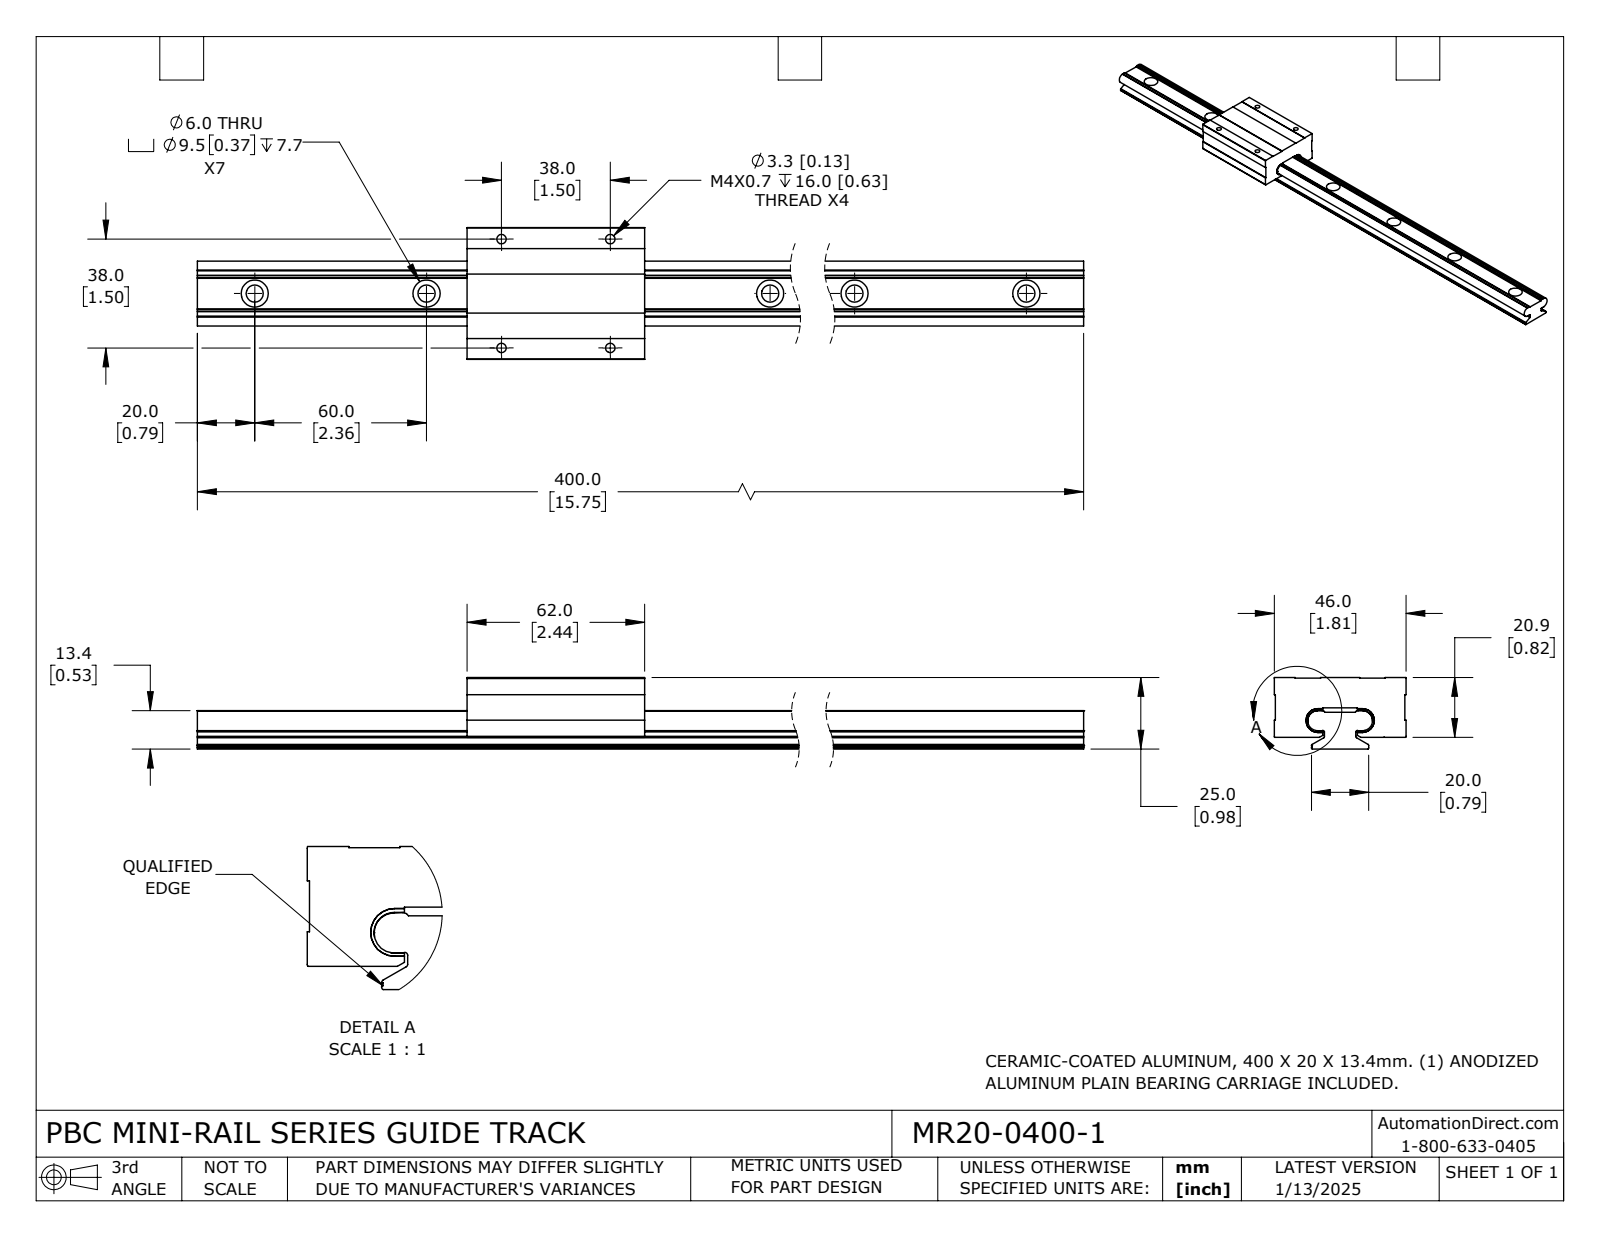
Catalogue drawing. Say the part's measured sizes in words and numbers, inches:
The part is named "MR20-0400-1; MR20-0400-1_RAIL; MR20-0400-1_CARRIAGE". Its 3-D file was written by "SolidWorks 2023 (CONFIG_CONTROL_DESIGN)". It is 4 solids with 150 faces: 84 planar, 66 cylindrical and 0 other. Overall it measures 15.748 by 1.811 by 0.984 inches. Its volume is 8.34 cubic inches and its surface area 79.98 square inches. Round holes: 7 of diameter 0.236, 7 of diameter 0.374, 4 of diameter 0.13. Partial cylindrical surfaces (rounded edges, fillets, slot ends): 10 of radius 0.02, 4 of radius 0.14, 2 of radius 0.04, 2 of radius 0.138, 2 of radius 0.138, 2 of radius 0.164, 1 of radius 0.005. The main face-to-face distances are 0.507, 0.16, 0.347, 0.984, 0.824, 0.477, 0.691, 1.12, 0.976, 0.815. The hole center spacings are 2.362, 4.724, 7.087, 9.449, 0.766, 1.274, 1.496, 1.496.
